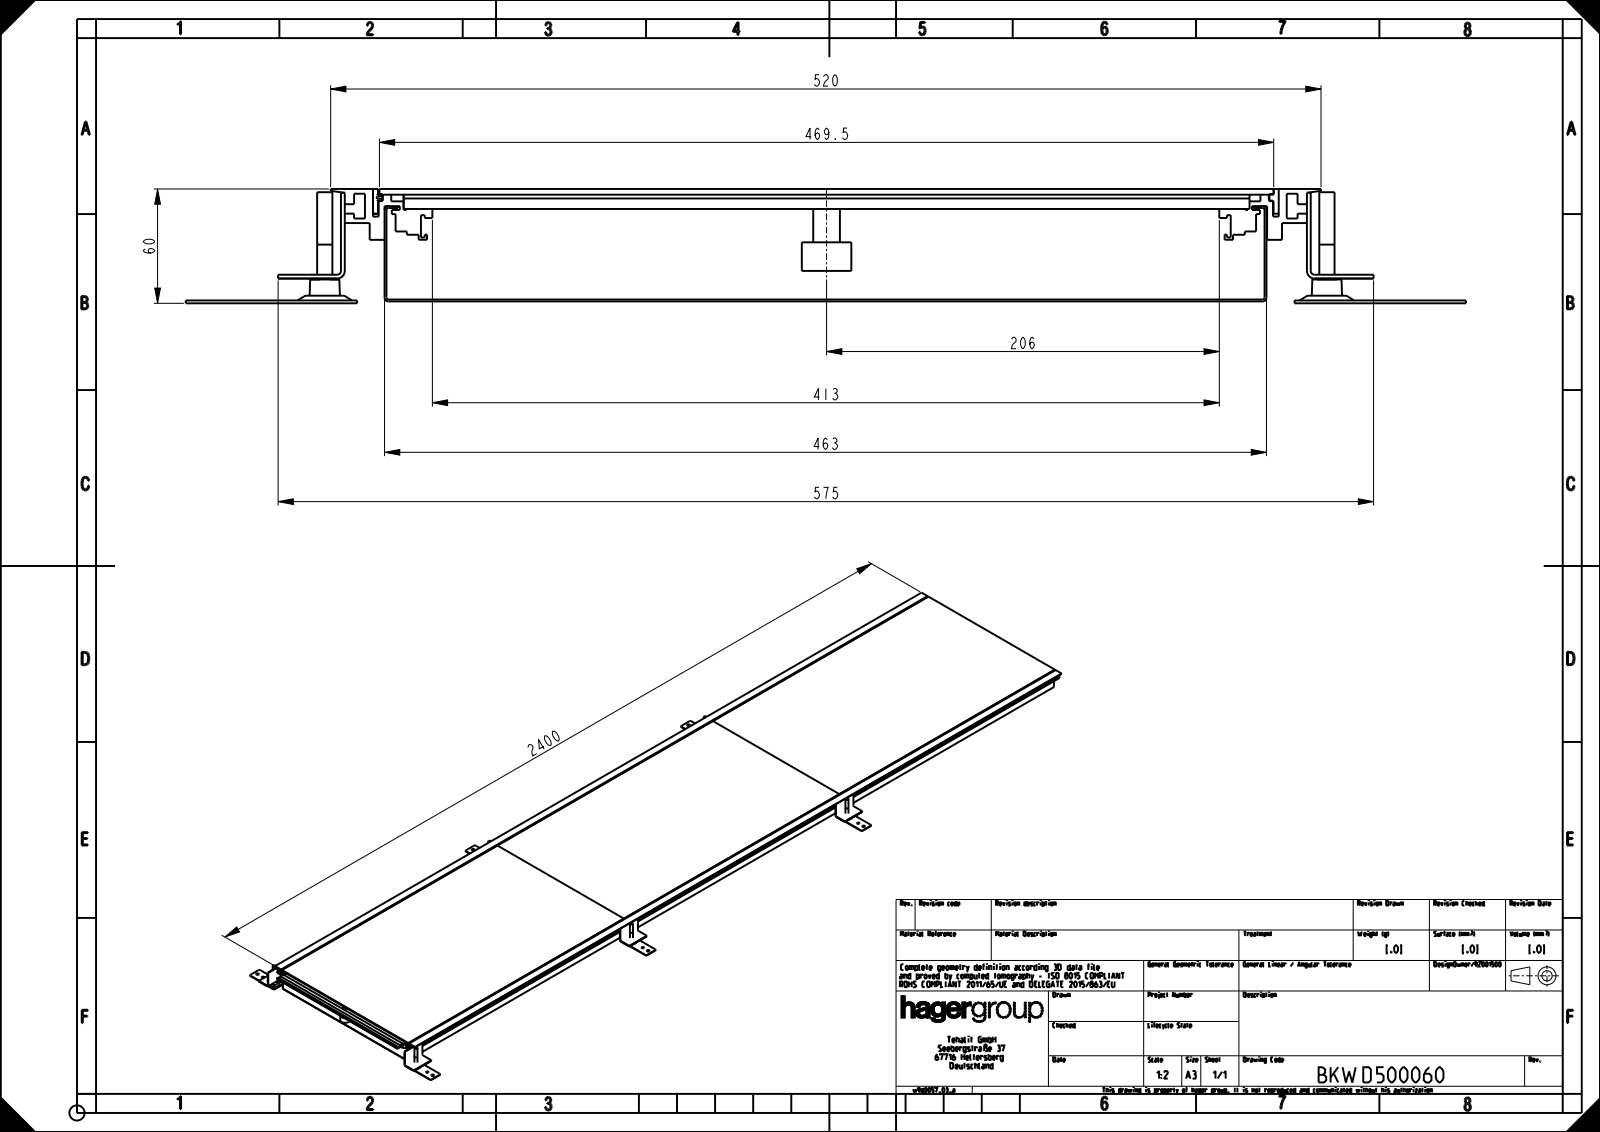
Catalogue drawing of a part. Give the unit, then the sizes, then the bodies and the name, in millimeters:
Units: millimetres
Overall size (bounding box): 2432.5 × 672.13 × 60
Round holes (diameter × count): ⌀7 ×15, ⌀8 ×9, ⌀10 ×9, ⌀6 ×6, ⌀8.5 ×6, ⌀11.5 ×6, ⌀17.5 ×6, ⌀23 ×6
Round bosses / shafts (diameter × count): ⌀26 ×9, ⌀14 ×9, ⌀11.9 ×9, ⌀20 ×6, ⌀8 ×6
Partial cylindrical surfaces — rounded edges, fillets, slot ends (radius × count): R2 ×96, R3 ×24, R0.5 ×20, R1 ×4, R4 ×2
Main face-to-face distances: 1, 3, 56, 59, 55, 58, 7.5, 6.5, 48.5, 47.5
Hole centre spacings: 800, 1600, 800.25, 801.1, 802.4, 981.21, 992.92, 1018.36
Volume: 9 034 000 mm³ · Surface area: 7 392 000 mm²
Bodies: 61 solids, 1036 faces (606 planar, 358 cylindrical, 72 other)
Part name (STEP PRODUCT): U05644KUN; U05650KUN; U05647KUN; U05826KUN (+8 more)
STEP written by: CREO PARAMETRIC BY PTC INC, 2020281 (AUTOMOTIVE_DESIGN)
